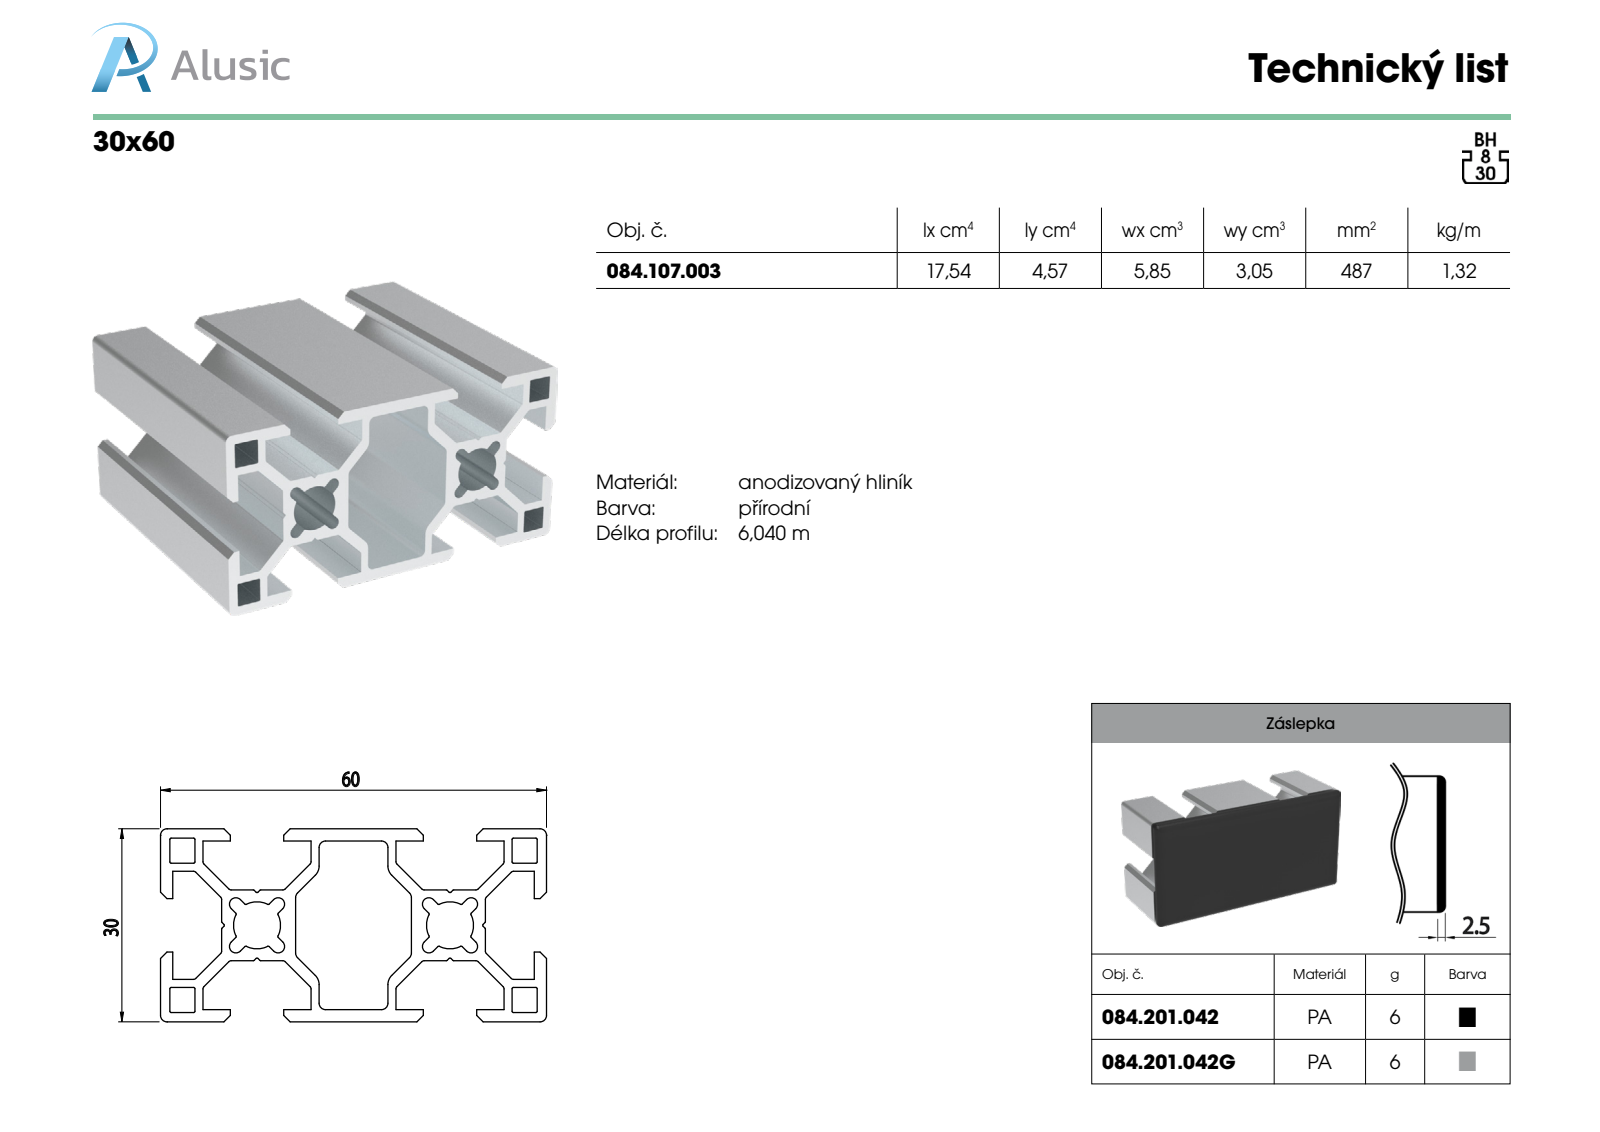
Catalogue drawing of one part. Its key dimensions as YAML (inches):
part_name: "084.201.042"
step_written_by: "SolidWorks 2012 (CONFIG_CONTROL_DESIGN)"
units: inches
bodies: {solids: 1, faces: 158, planar: 38, cylindrical: 58, other: 62}
overall_size: [2.362, 1.181, 0.295]
volume: 0.281
surface_area: 6.891
round_holes:
  - {diameter: 0.087, count: 4}
round_bosses_or_shafts:
  - {diameter: 0.142, count: 4}
partial_cylinders:
  - {radius: 0.012, count: 14}
  - {radius: 0.039, count: 4}
  - {radius: 0.079, count: 4}
  - {radius: 0.144, count: 2}
face_to_face_distances: [0.098, 0.567, 0.614, 0.047, 1.181, 1.748, 1.795, 0.1, 1.228, 1.134]
hole_center_spacings: [0.913, 2.094, 2.285]
